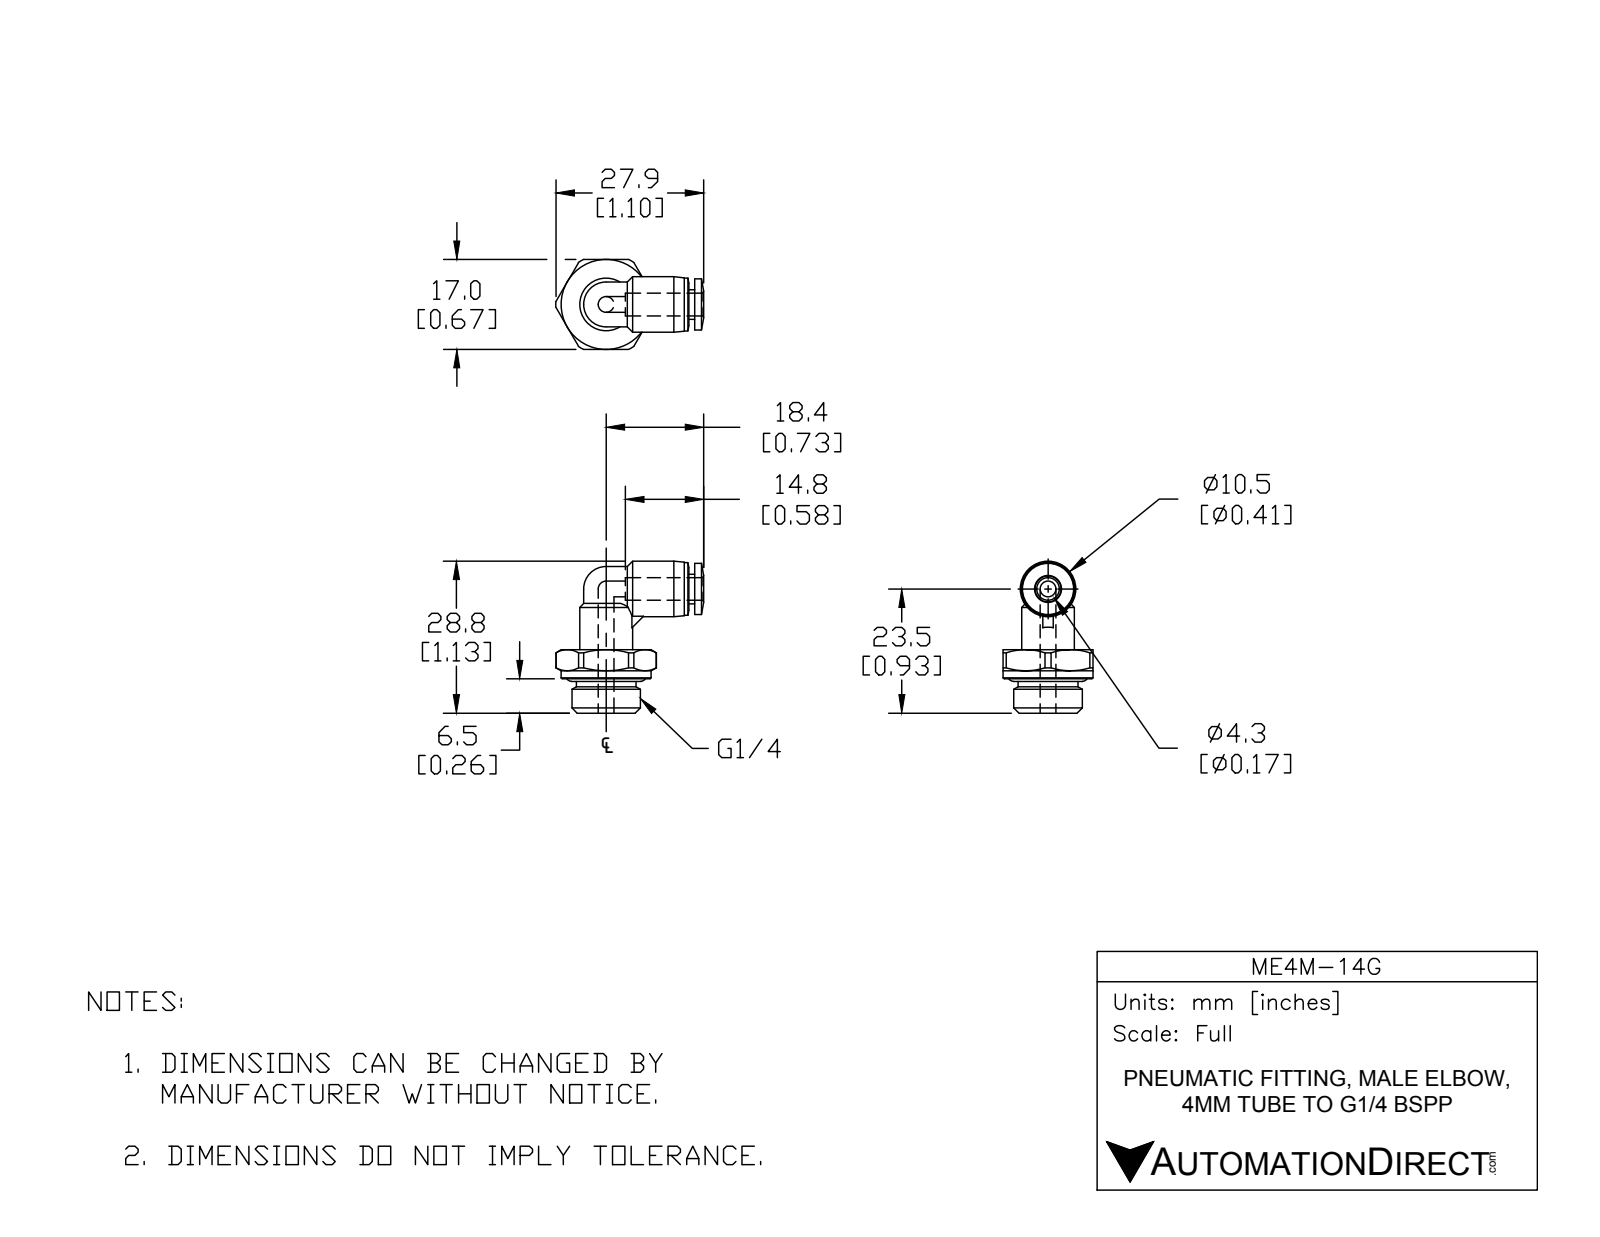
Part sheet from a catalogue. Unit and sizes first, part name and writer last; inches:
Units: inches
Overall size (bounding box): 1.132 × 1.1 × 0.669
Round holes (diameter × count): ⌀0.118 ×1, ⌀0.169 ×1
Round bosses / shafts (diameter × count): ⌀0.394 ×2, ⌀0.669 ×1, ⌀0.51 ×1, ⌀0.445 ×1, ⌀0.413 ×1, ⌀0.382 ×1, ⌀0.22 ×1
Partial cylindrical surfaces — rounded edges, fillets, slot ends (radius × count): R0.167 ×2, R0.374 ×1
Main face-to-face distances: 0.669, 0.472, 0.311, 0.161, 0.256, 0.055, 0.217, 0.043, 0.315, 0.059
Volume: 0.237 in³ · Surface area: 4.387 in²
Bodies: 2 solids, 78 faces (21 planar, 32 cylindrical, 25 other)
Part name (STEP PRODUCT): ME4M-14G
STEP written by: SolidWorks 2021 (CONFIG_CONTROL_DESIGN)
